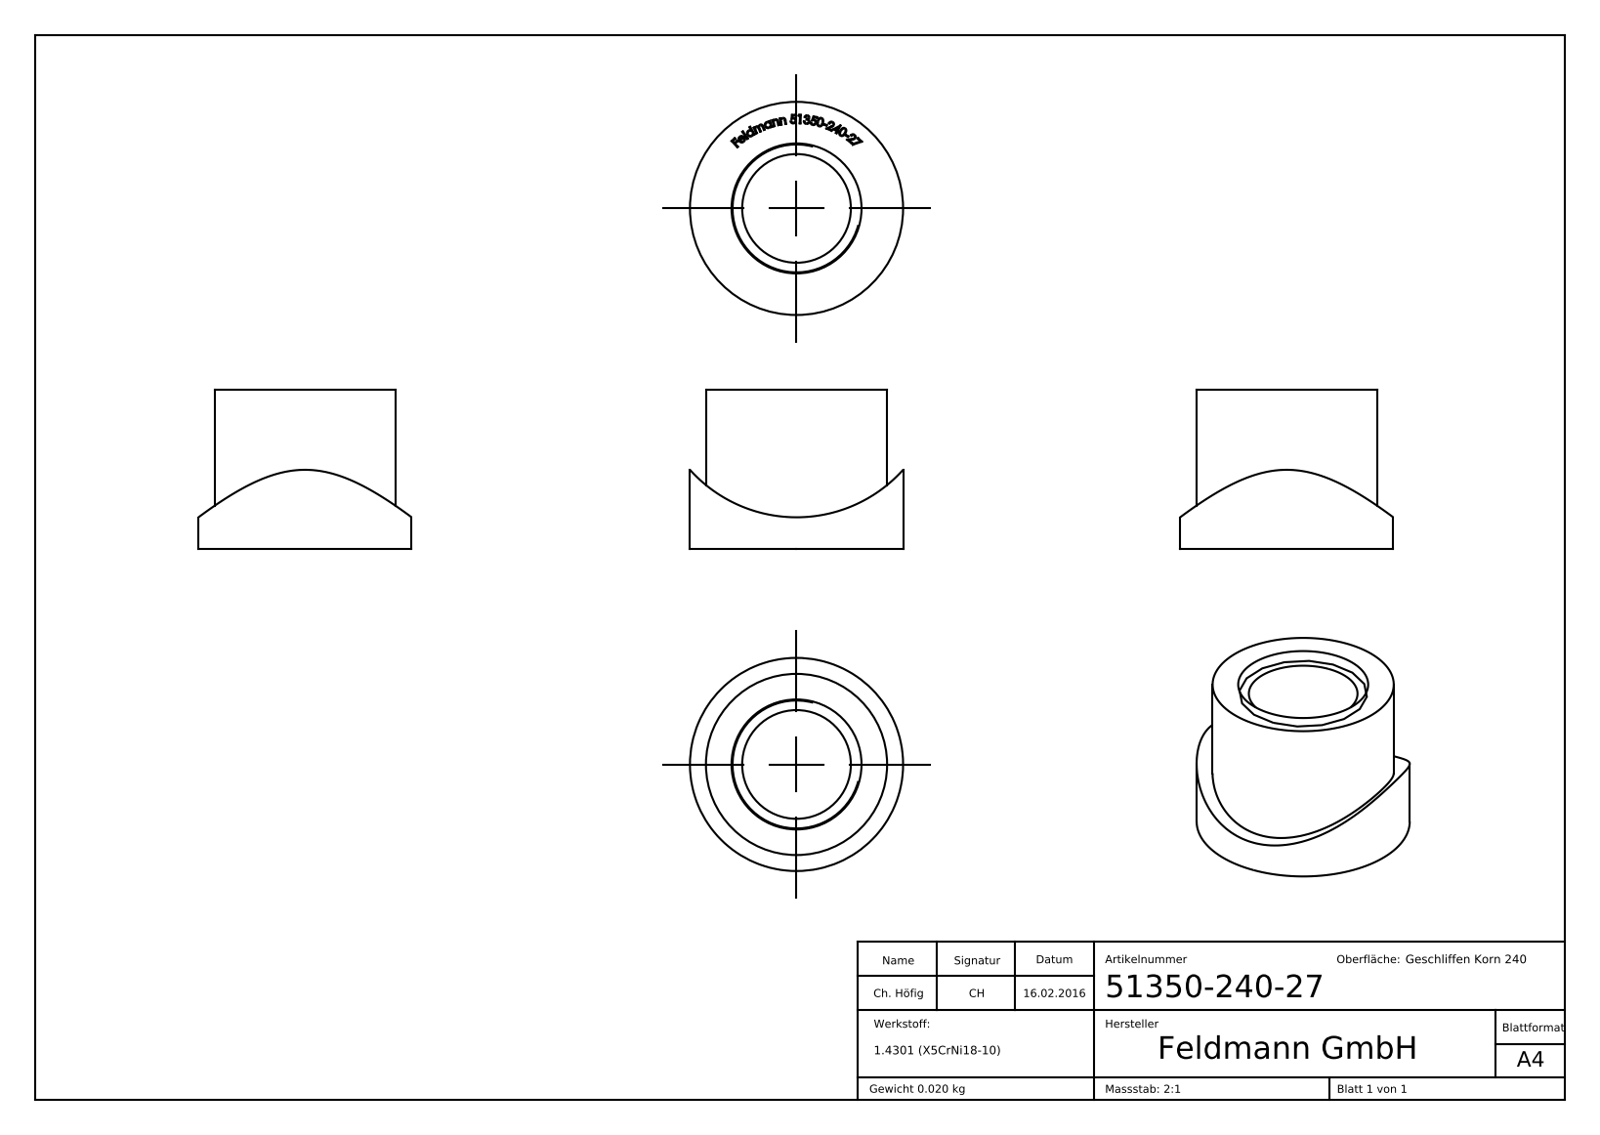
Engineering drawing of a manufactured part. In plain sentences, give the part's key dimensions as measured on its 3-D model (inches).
The part is named "51350-240-27". Its 3-D file was written by "SolidWorks 2015 (CONFIG_CONTROL_DESIGN)". It is 1 solid with 261 faces: 142 planar, 7 cylindrical and 112 other. Overall it measures 0.787 by 0.787 by 0.591 inches. Its volume is 0.156 cubic inches and its surface area 2.815 square inches. Round holes: 1 of diameter 0.402. Round bosses or shafts: 1 of diameter 0.787, 1 of diameter 0.669. Partial cylindrical surfaces (rounded edges, fillets, slot ends): 1 of radius 0.53. The main face-to-face distances are 0.591, 0.587, 0.016, 0.013, 0.02, 0.019, 0.031, 0.014, 0.034, 0.031.
